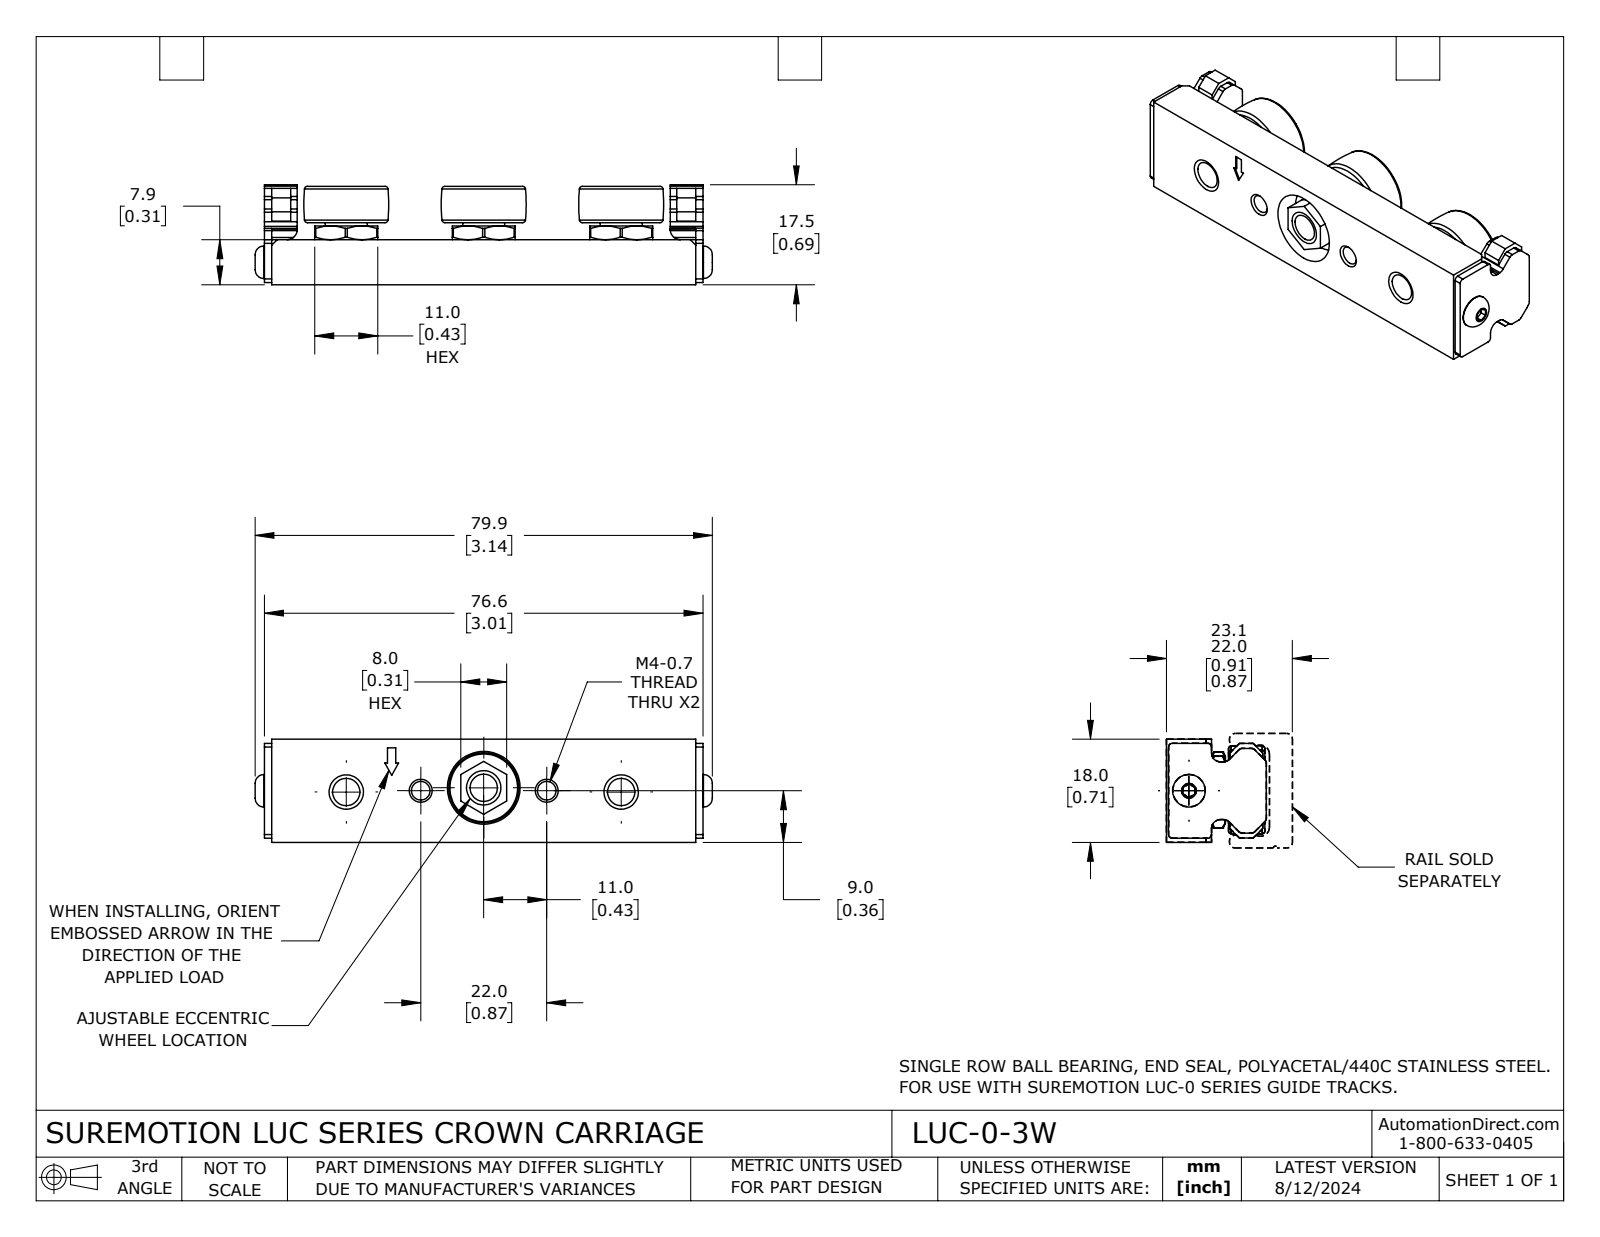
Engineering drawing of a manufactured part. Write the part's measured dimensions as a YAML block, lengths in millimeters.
part_name: "LUC-0-3W"
step_written_by: "SolidWorks 2023 (CONFIG_CONTROL_DESIGN)"
units: millimeters
bodies: {solids: 7, faces: 466, planar: 198, cylindrical: 142, other: 126}
overall_size: [79.9, 18, 17.4]
volume: 15500
surface_area: 10000
round_holes:
  - {diameter: 9.9, count: 3}
  - {diameter: 3.3, count: 2}
  - {diameter: 4.9, count: 2}
  - {diameter: 2.5, count: 1}
  - {diameter: 4.9, count: 1}
  - {diameter: 5.6, count: 1}
  - {diameter: 12.7, count: 1}
round_bosses_or_shafts:
  - {diameter: 7.3, count: 3}
  - {diameter: 6, count: 3}
  - {diameter: 4.5, count: 3}
  - {diameter: 11.8, count: 1}
  - {diameter: 5.7, count: 1}
  - {diameter: 3, count: 1}
partial_cylinders:
  - {radius: 0.4, count: 12}
  - {radius: 0.8, count: 6}
  - {radius: 0.6, count: 4}
  - {radius: 1.6, count: 4}
  - {radius: 6.2, count: 3}
  - {radius: 1.8, count: 2}
face_to_face_distances: [7.9, 18, 1.3, 75.3, 5.3, 1.1, 74, 8.3, 16.1, 76.6]
hole_center_spacings: [11, 13, 24, 35, 22, 48]
